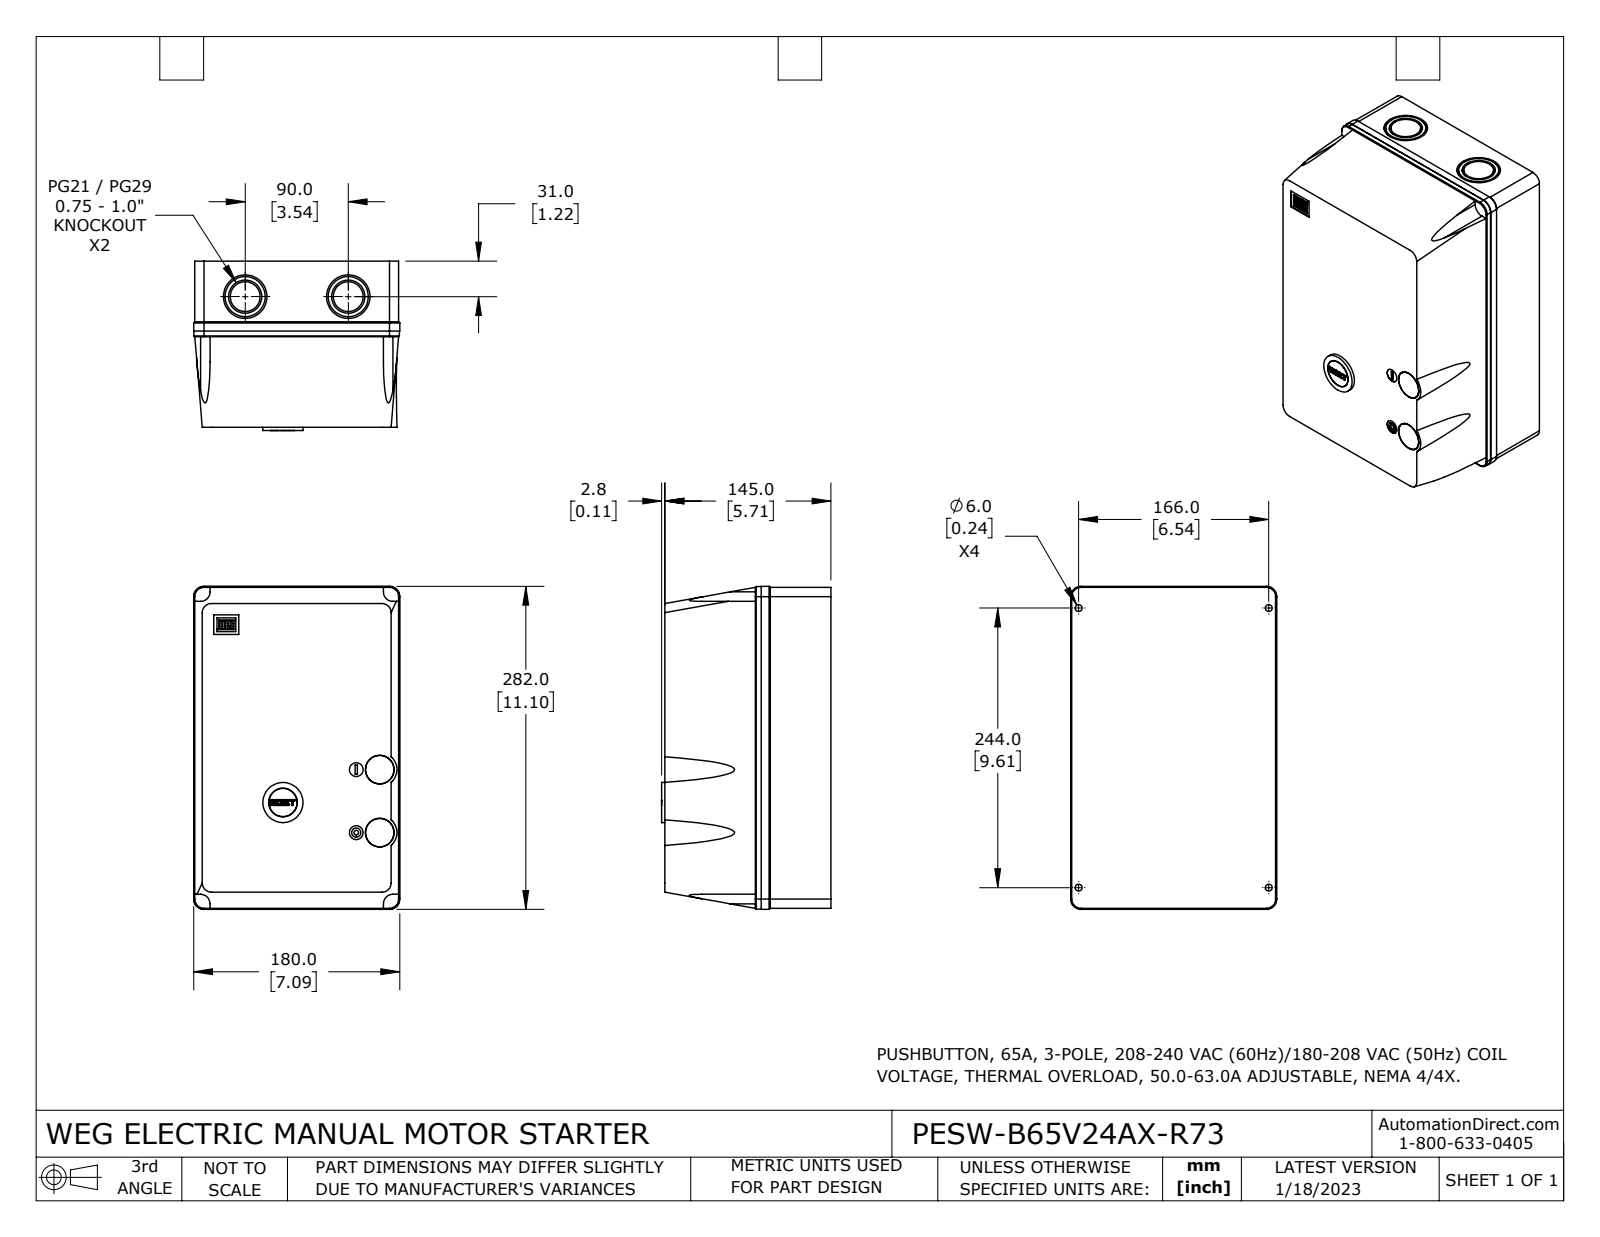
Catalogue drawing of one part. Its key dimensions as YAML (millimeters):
part_name: "PESW-B65V24AX-R73"
step_written_by: "SolidWorks 2021 (CONFIG_CONTROL_DESIGN)"
units: millimeters
bodies: {solids: 3, faces: 286, planar: 130, cylindrical: 144, other: 12}
overall_size: [282, 180, 147.9]
volume: 7014000
surface_area: 232257
round_holes:
  - {diameter: 6, count: 4}
  - {diameter: 25, count: 3}
  - {diameter: 12, count: 2}
  - {diameter: 29, count: 2}
  - {diameter: 38, count: 2}
  - {diameter: 4, count: 1}
  - {diameter: 30.5, count: 1}
round_bosses_or_shafts:
  - {diameter: 35, count: 3}
  - {diameter: 26, count: 2}
  - {diameter: 24.8, count: 2}
  - {diameter: 30.3, count: 1}
  - {diameter: 24.6, count: 1}
  - {diameter: 14, count: 1}
  - {diameter: 8, count: 1}
partial_cylinders:
  - {radius: 0.1, count: 34}
  - {radius: 8, count: 4}
  - {radius: 8.3, count: 4}
  - {radius: 8.7, count: 4}
  - {radius: 9, count: 4}
  - {radius: 1.6, count: 1}
face_to_face_distances: [145, 178, 280, 1, 0.7, 179, 179.7, 178.7, 281, 180]
hole_center_spacings: [20.5, 55, 58.7, 166, 244, 295.11, 49.14, 57.14]
